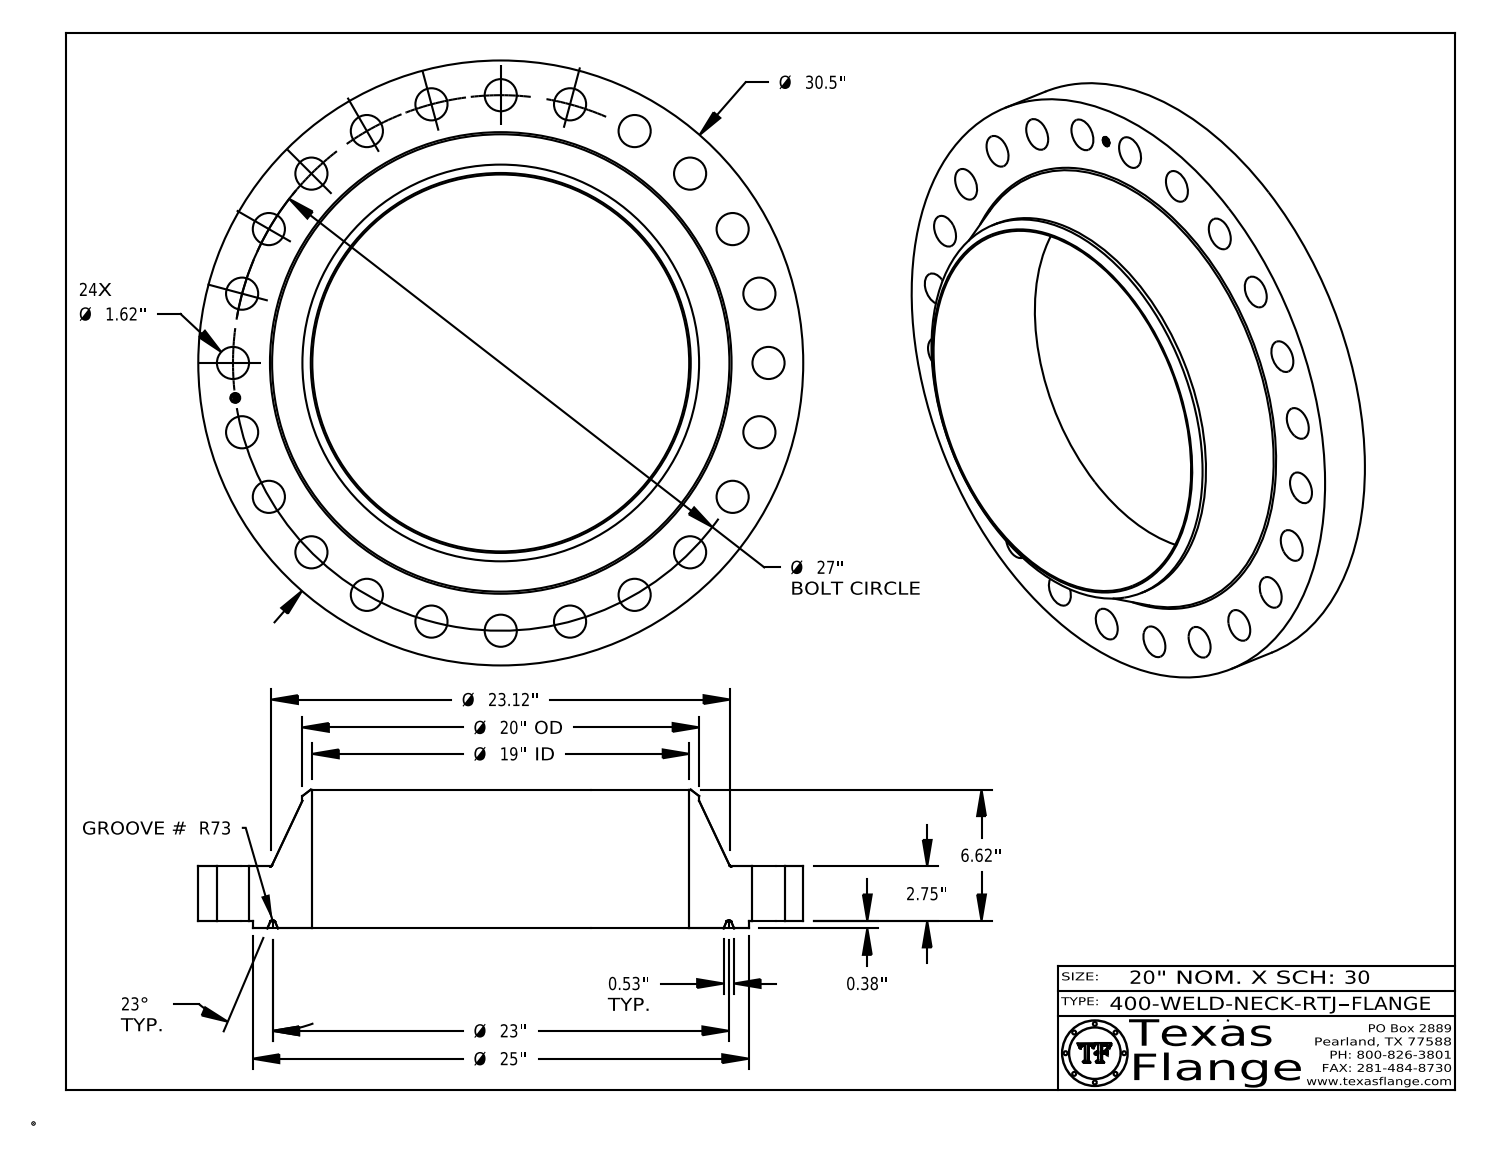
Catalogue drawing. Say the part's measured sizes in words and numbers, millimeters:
The part is named "400-WELD-NECK-RTJ". Its 3-D file was written by "CATIA V5 STEP AP214 (AUTOMOTIVE_DESIGN)". It is 1 solid with 461 faces: 371 planar, 76 cylindrical and 14 other. Overall it measures 774.7 by 774.7 by 177.7 millimeters. Its volume is 23 700 000 cubic millimeters and its surface area 1 315 000 square millimeters. Round holes: 24 of diameter 41.1, 1 of diameter 12.6, 1 of diameter 482.6. Round bosses or shafts: 8 of diameter 0.8, 1 of diameter 774.7, 1 of diameter 635, 1 of diameter 508, 1 of diameter 9.9. The main face-to-face distances are 69.9, 9.5, 79.4, 177.7, 168.1, 98.3, 79, 69.5, 0.4, 98.7. The hole center spacings are 342.9, 89.5, 177.5, 262.5, 417.5, 633.6, 679.9, 544.1.
